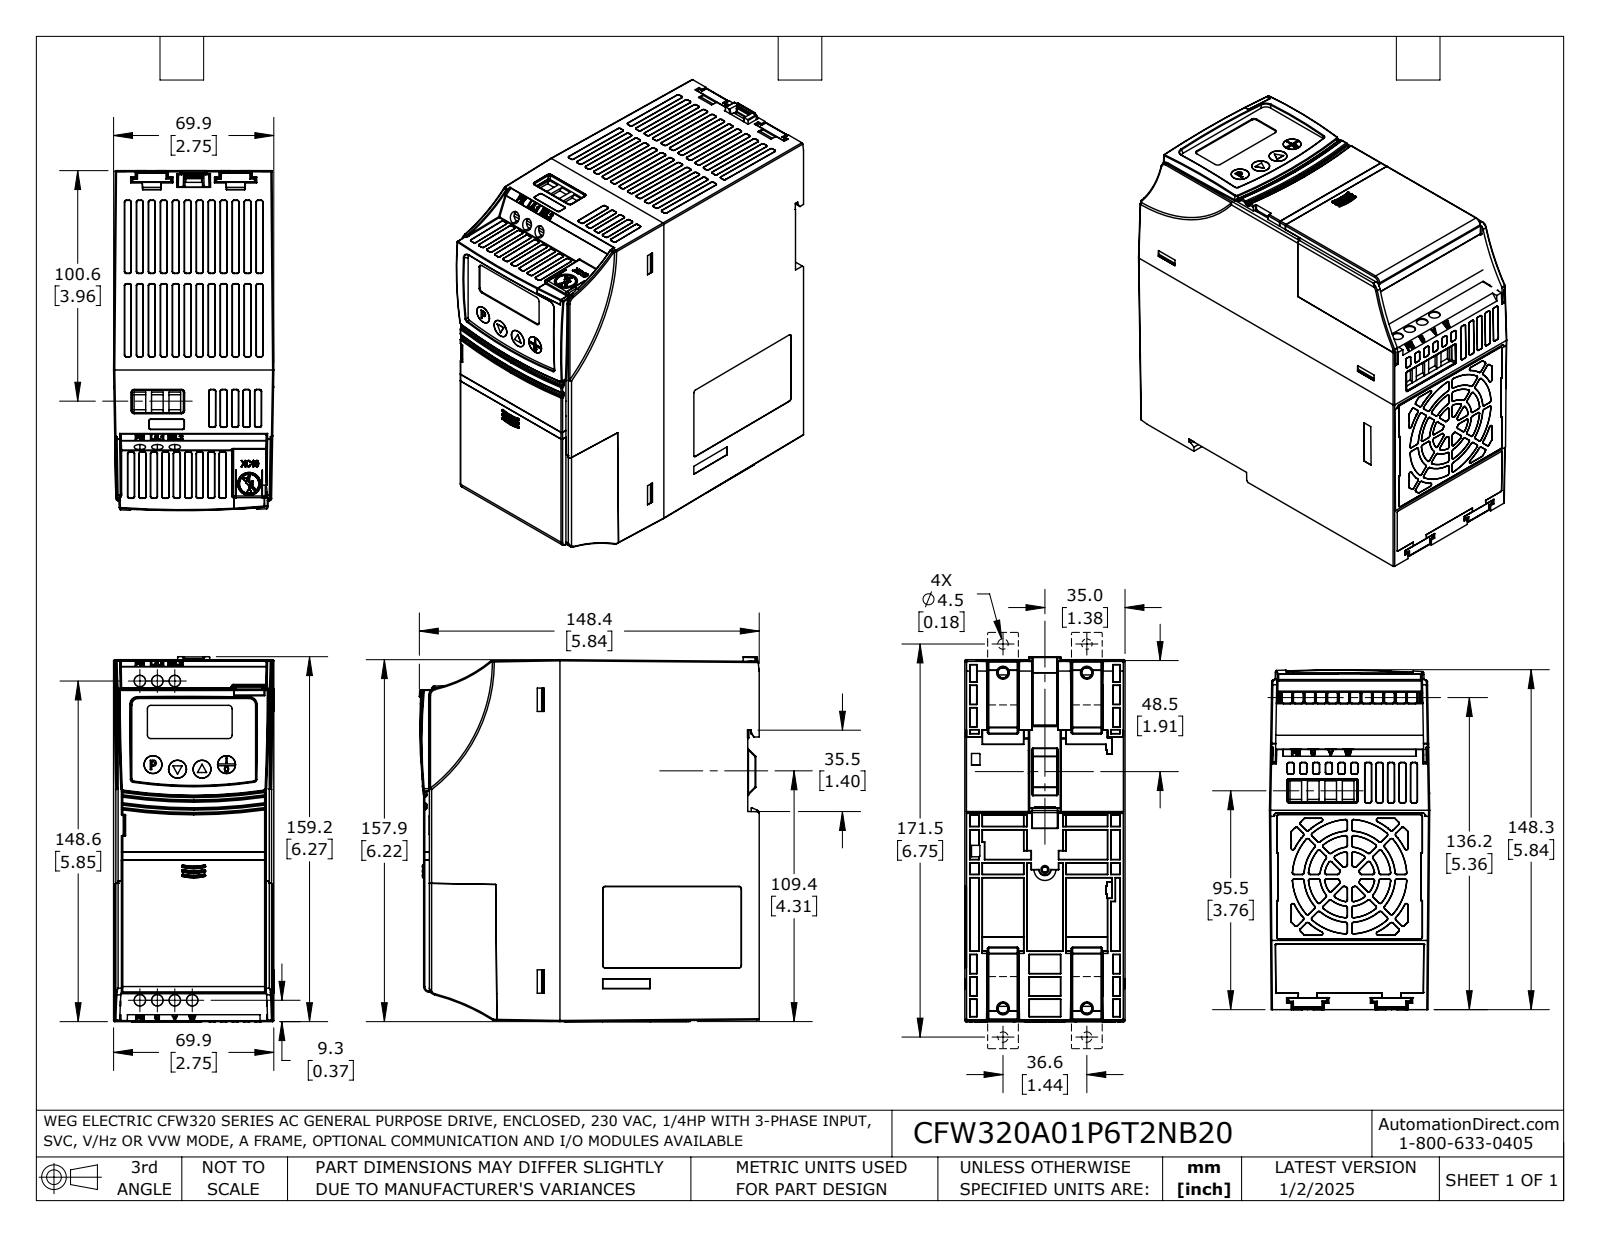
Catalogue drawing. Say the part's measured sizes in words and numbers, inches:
The part is named "CFW320A01P6T2NB20". Its 3-D file was written by "SolidWorks 2021 (AUTOMOTIVE_DESIGN)". It is 6 solids with 3715 faces: 1587 planar, 853 cylindrical and 1275 other. Overall it measures 6.269 by 5.841 by 2.754 inches. Its volume is 15.24 cubic inches and its surface area 309 square inches. Round holes: 3 of diameter 0.197. Partial cylindrical surfaces (rounded edges, fillets, slot ends): 327 of radius 0.012, 150 of radius 0.02, 13 of radius 0.039, 5 of radius 0.03, 3 of radius 0.118, 2 of radius 0.01, 1 of radius 0.098, 1 of radius 0.126. The main face-to-face distances are 0.07, 0.055, 0.019, 0.05, 6, 5.33, 5.275, 5.571, 5.516, 0.241. The hole center spacings are 0.3, 0.6.
